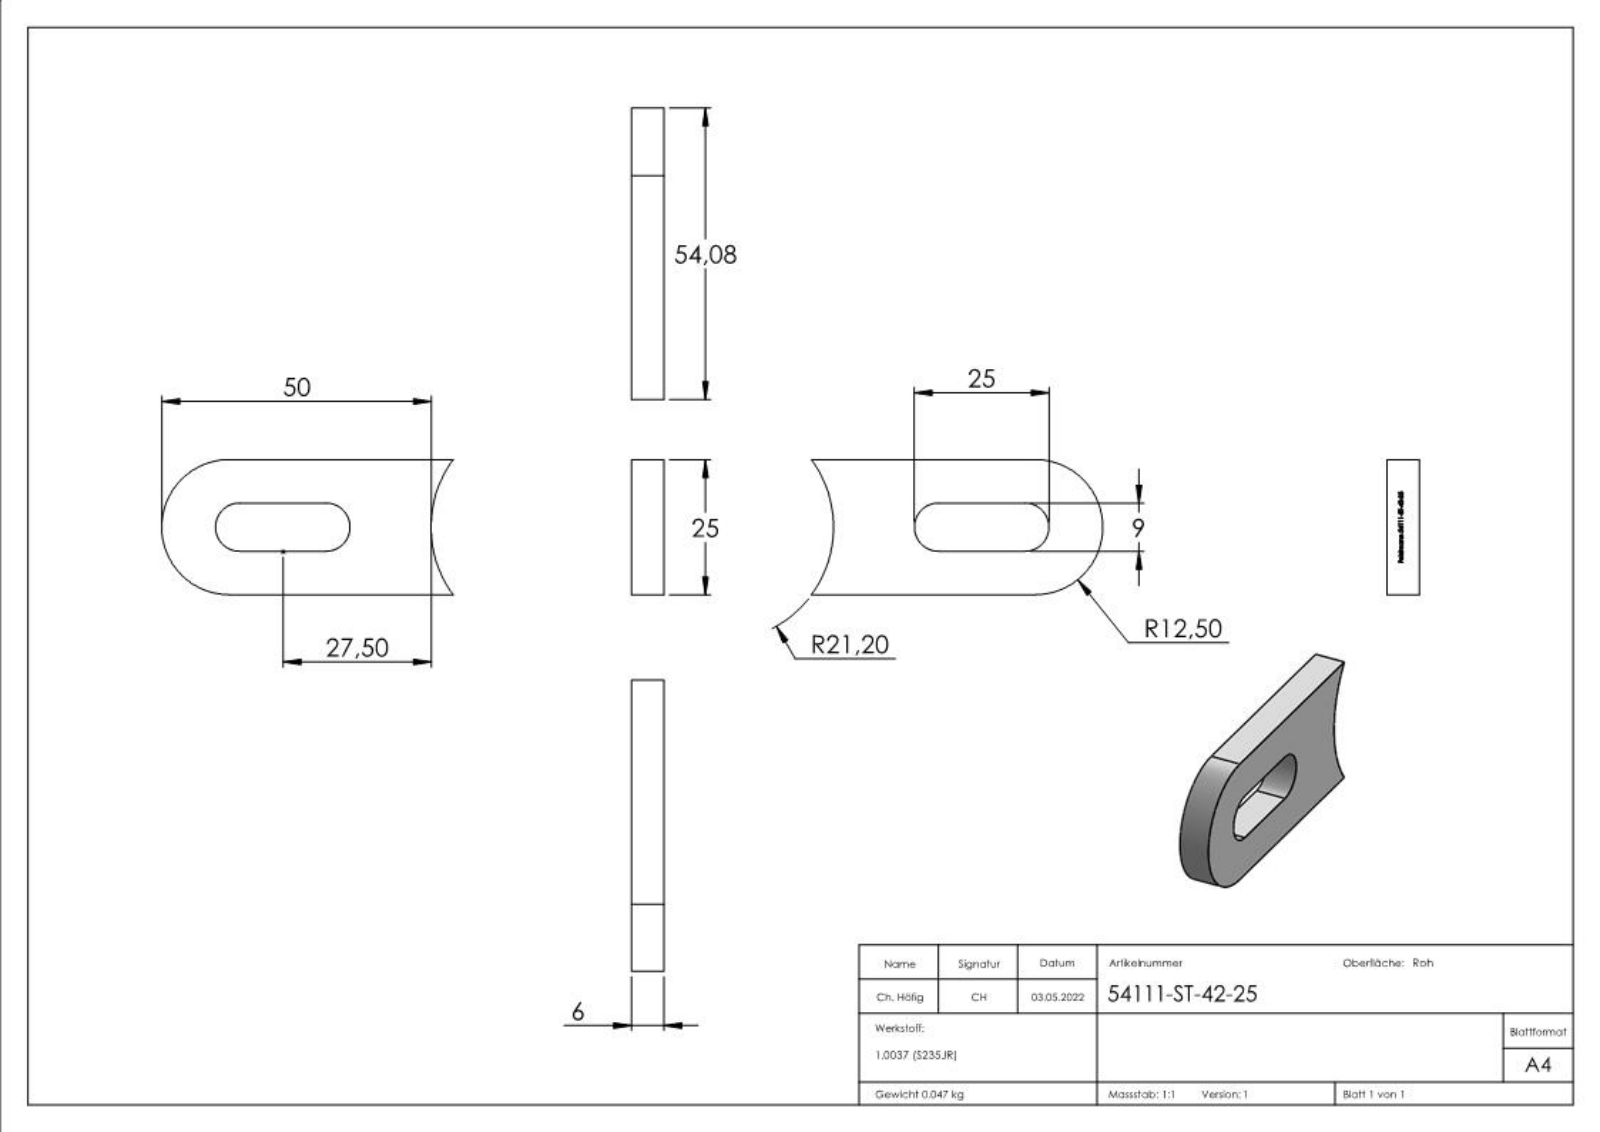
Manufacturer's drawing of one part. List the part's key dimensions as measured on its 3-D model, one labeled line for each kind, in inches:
Part name (STEP PRODUCT): 54111-ST-42-25
STEP written by: SolidWorks 2018 (CONFIG_CONTROL_DESIGN)
Units: inches
Bodies: 1 solid, 272 faces (150 planar, 31 cylindrical, 91 other)
Overall size (bounding box): 2.129 × 0.984 × 0.236
Volume: 0.369 in³ · Surface area: 5.082 in²
Partial cylindrical surfaces — rounded edges, fillets, slot ends (radius × count): R0.177 ×2, R0.492 ×1, R0.835 ×1, R0.839 ×1
Main face-to-face distances: 0.236, 0.984, 0.315, 0.669, 0.354, 0.118, 0.021, 0.024, 0.028, 0.149
